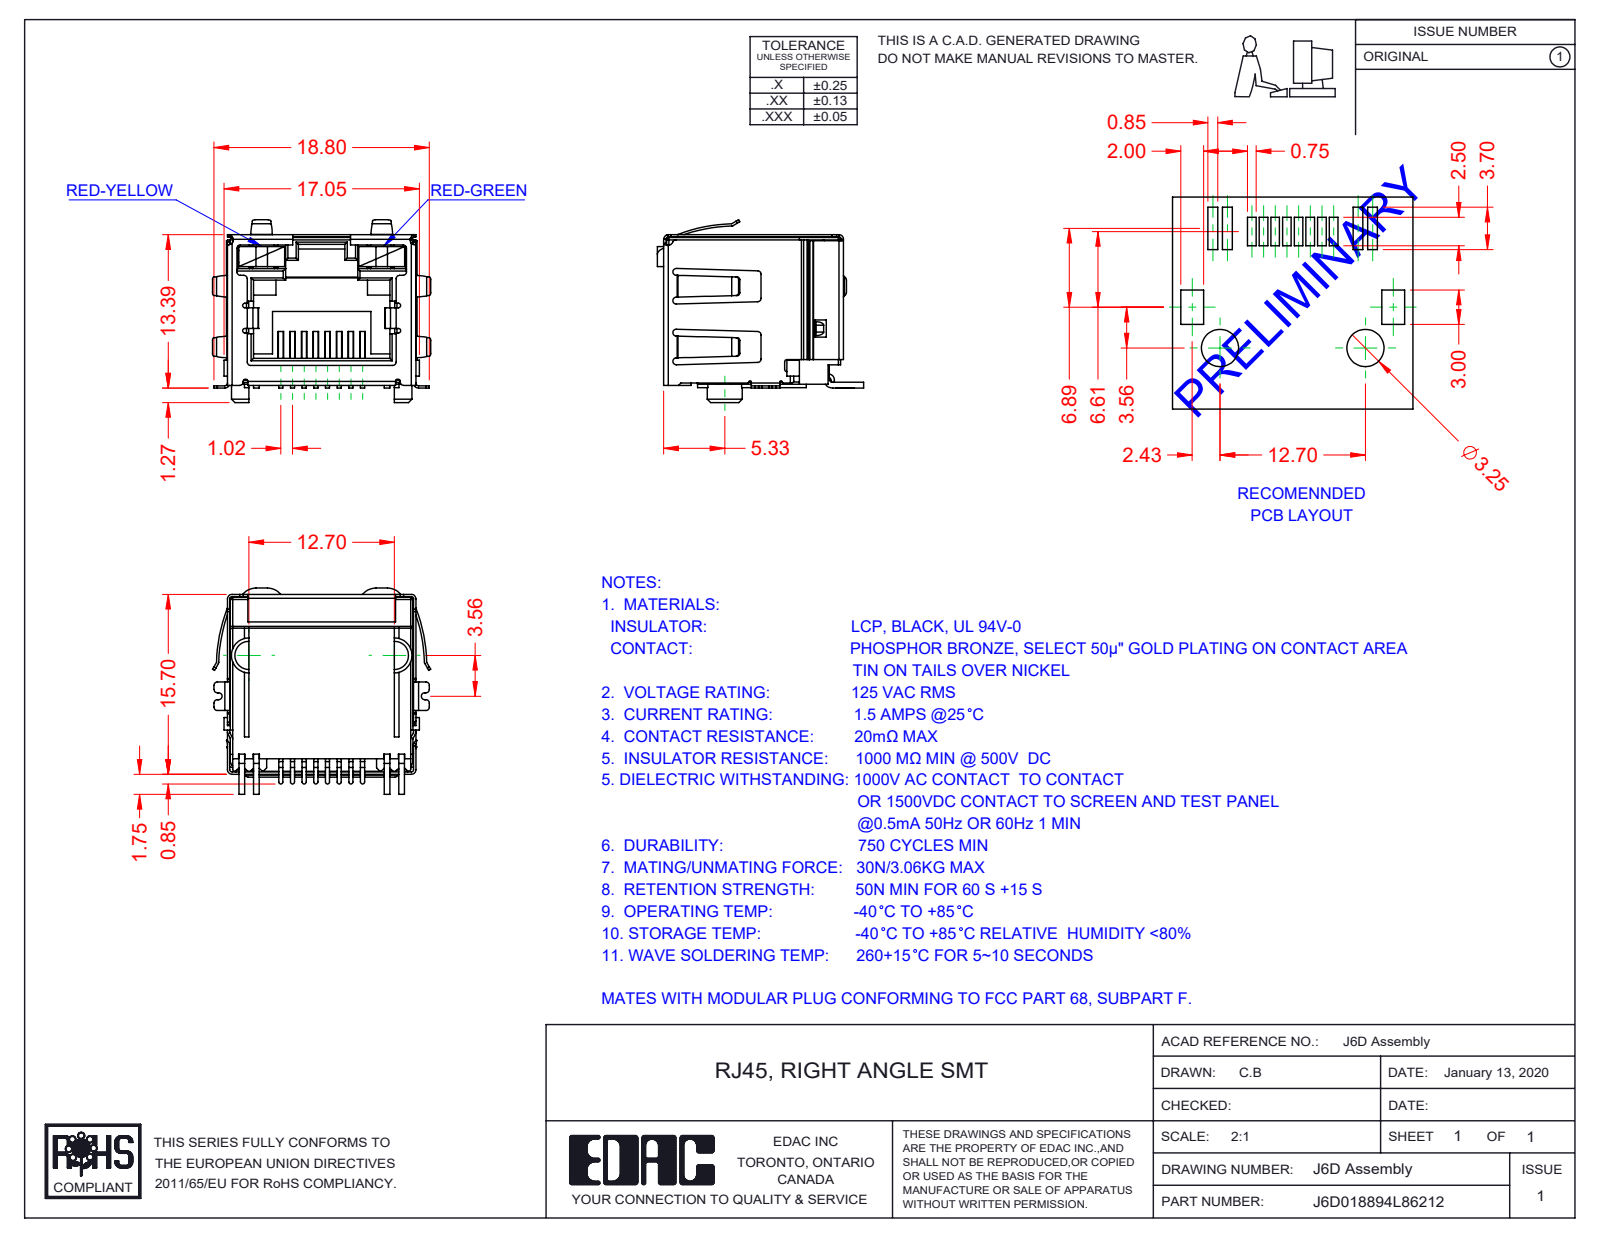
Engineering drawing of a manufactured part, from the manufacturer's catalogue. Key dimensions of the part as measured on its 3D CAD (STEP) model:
Part name (STEP PRODUCT): 6D Insulator; 6D LED RH_6-Red-Green; 6D LED LH_8-Red-Yellow; 6D Contacts (+2 more)
STEP written by: SolidWorks 2016 (CONFIG_CONTROL_DESIGN)
Units: millimetres
Bodies: 12 solids, 1034 faces (703 planar, 286 cylindrical, 45 other)
Overall size (bounding box): 19.06 × 18 × 15.95
Volume: 1 790 mm³ · Surface area: 4 796 mm²
Partial cylindrical surfaces — rounded edges, fillets, slot ends (radius × count): R0.3 ×55, R0.2 ×40, R0.4 ×19, R0.25 ×16, R0.1 ×12, R0.15 ×8, R0.18 ×8, R0.5 ×6
Main face-to-face distances: 16, 16.2, 16.25, 2.25, 1, 15.95, 12.8, 0.45, 13.05, 10.6
